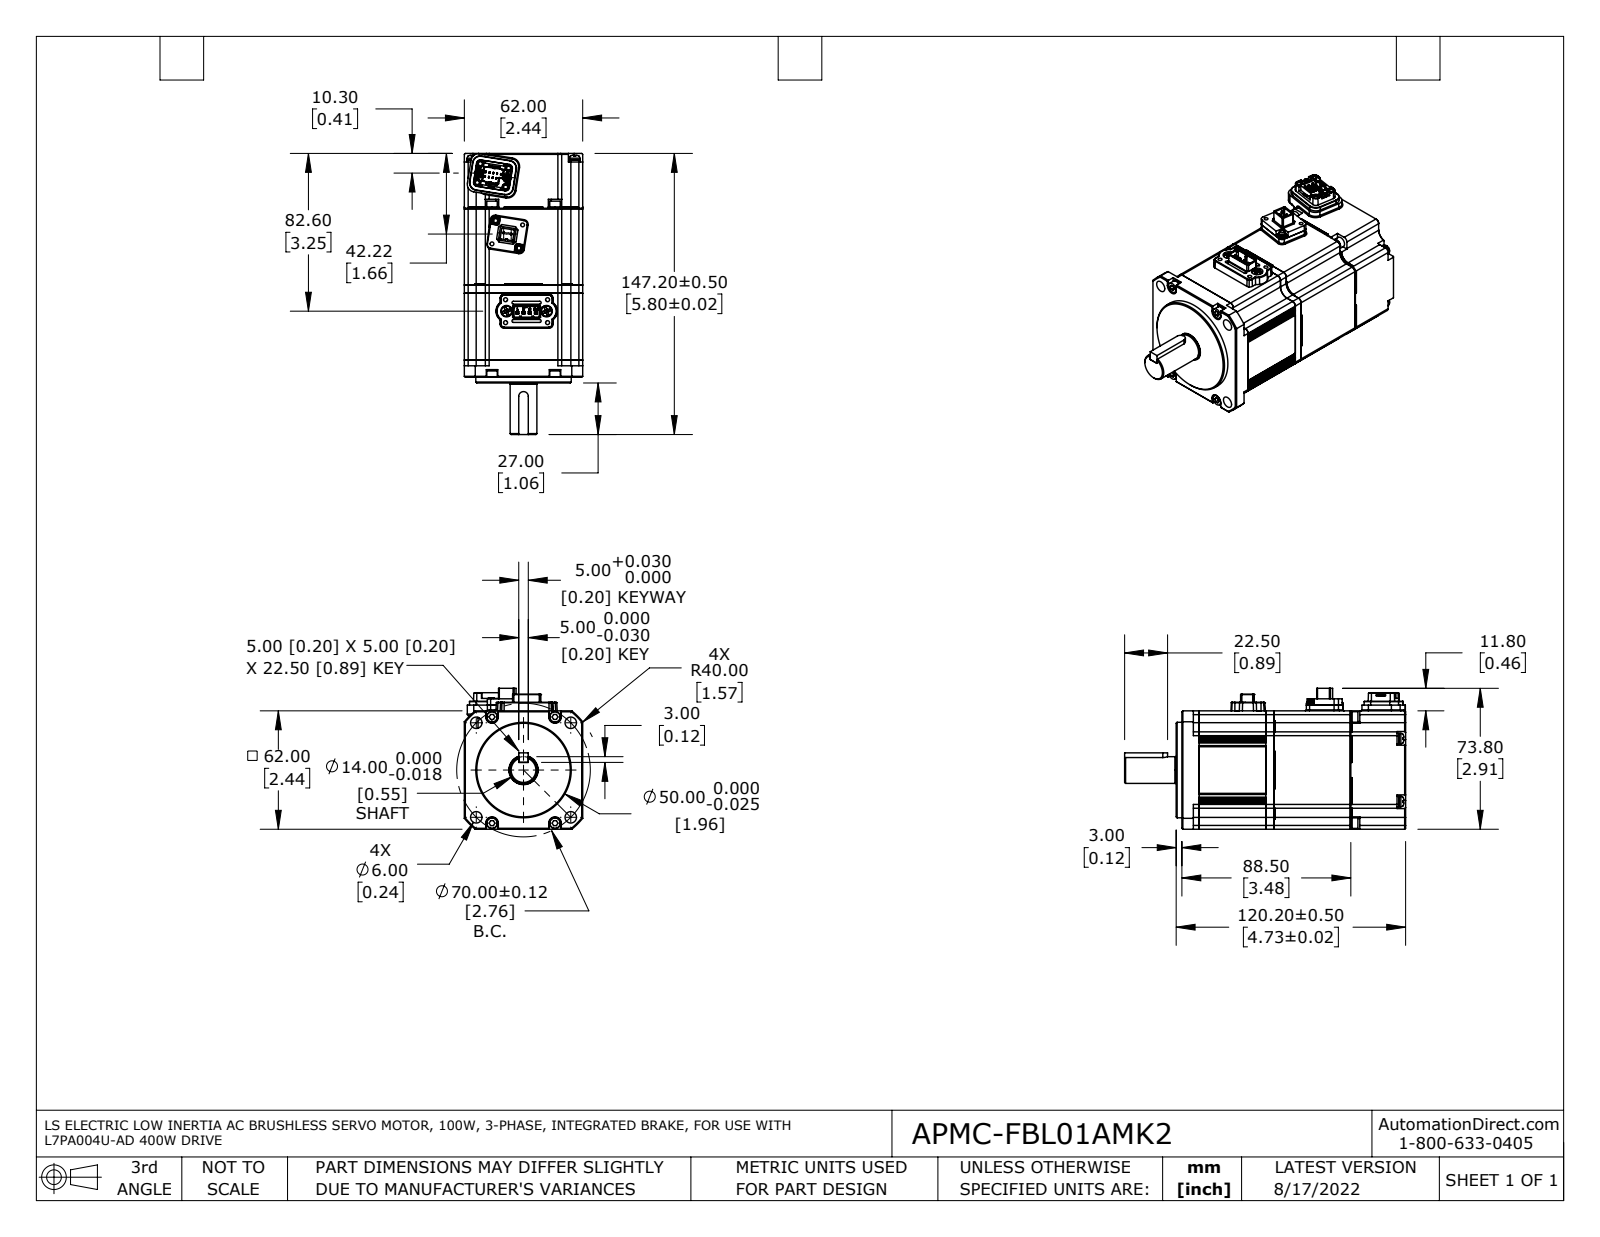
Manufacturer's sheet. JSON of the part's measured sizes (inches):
{"part_name": "SLM06GA003G01_Out Line(APMC-FBL01AMK2) r1 nc fxt", "step_written_by": "SolidWorks 2017 (AUTOMOTIVE_DESIGN)", "units": "inches", "bodies": {"solids": 51, "faces": 2103, "planar": 1289, "cylindrical": 602, "other": 212}, "overall_size": [5.795, 2.906, 2.441], "volume_in3": 25.14, "surface_area_in2": 148.8, "round_holes": [[0.083, 10], [0.118, 10], [0.138, 8], [0.079, 6], [0.236, 6], [0.122, 4], [0.039, 2], [0.13, 1], [0.134, 1], [0.512, 1], [0.602, 1]], "round_bosses_or_shafts": [[0.213, 6], [0.22, 4], [0.217, 4], [0.165, 2], [0.142, 2], [0.138, 2], [0.087, 2], [0.035, 2]], "partial_cylinders_radius": [[0.008, 20], [0.012, 20], [0.039, 14], [0.079, 12], [0.006, 9], [0.118, 8], [0.018, 7], [0.004, 6]], "face_to_face_distances": [2.441, 0.169, 1.378, 0.02, 0.028, 1.547, 1.752, 1.583, 3.13, 1.61], "hole_center_spacings": [0.237, 0.335, 0.346, 0.371, 0.602, 0.63, 0.879, 1.239]}
